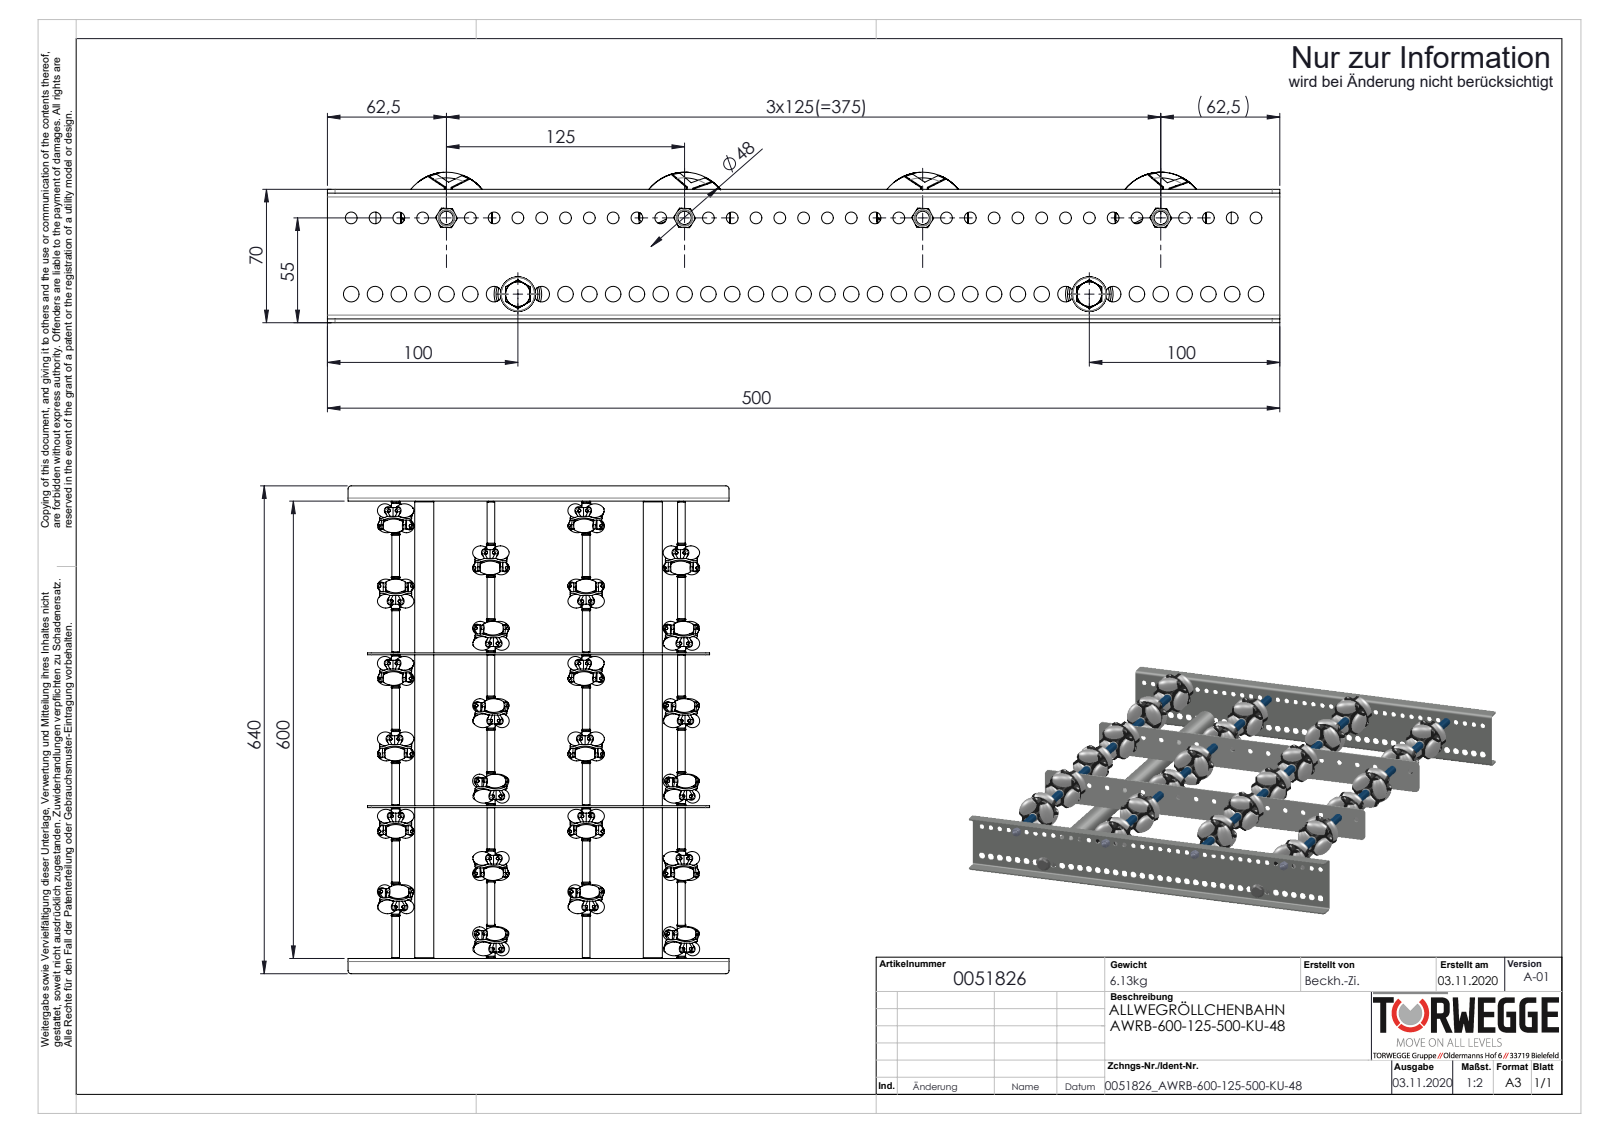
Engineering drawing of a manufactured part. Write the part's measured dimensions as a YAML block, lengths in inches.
part_name: "S100994_Sperrzahnschraube_M08x16-8.8-A2K; 0027528_BUCHSE-HOHLNIETE ZU AWR48; 0019719_Gewindestange-M6_L=620; Traversen_KFG_L600 (+8 more)"
step_written_by: "SolidWorks 2020 (AUTOMOTIVE_DESIGN)"
units: inches
bodies: {solids: 410, faces: 7476, planar: 2556, cylindrical: 2984, other: 1936}
overall_size: [25.197, 19.685, 3.11]
volume: 99.83
surface_area: 1851
round_holes:
  - {diameter: 0.146, count: 144}
  - {diameter: 0.165, count: 144}
  - {diameter: 0.244, count: 39}
  - {diameter: 0.323, count: 39}
  - {diameter: 0.256, count: 18}
  - {diameter: 0.194, count: 4}
  - {diameter: 0.331, count: 4}
  - {diameter: 0.268, count: 2}
  - {diameter: 0.827, count: 2}
round_bosses_or_shafts:
  - {diameter: 0.157, count: 144}
  - {diameter: 0.146, count: 126}
  - {diameter: 0.315, count: 6}
  - {diameter: 1.854, count: 4}
  - {diameter: 1.654, count: 4}
  - {diameter: 0.433, count: 4}
  - {diameter: 0.394, count: 4}
  - {diameter: 0.276, count: 4}
partial_cylinders:
  - {radius: 0.157, count: 8}
  - {radius: 0.079, count: 4}
  - {radius: 0.197, count: 4}
face_to_face_distances: [0.079, 23.701, 7.894, 0.098, 2.677, 0.581, 23.78, 23.622, 0.118, 0.463]
hole_center_spacings: [1.42, 1.419, 0.492, 0.984, 1.419, 1.476, 1.969, 2.461]
